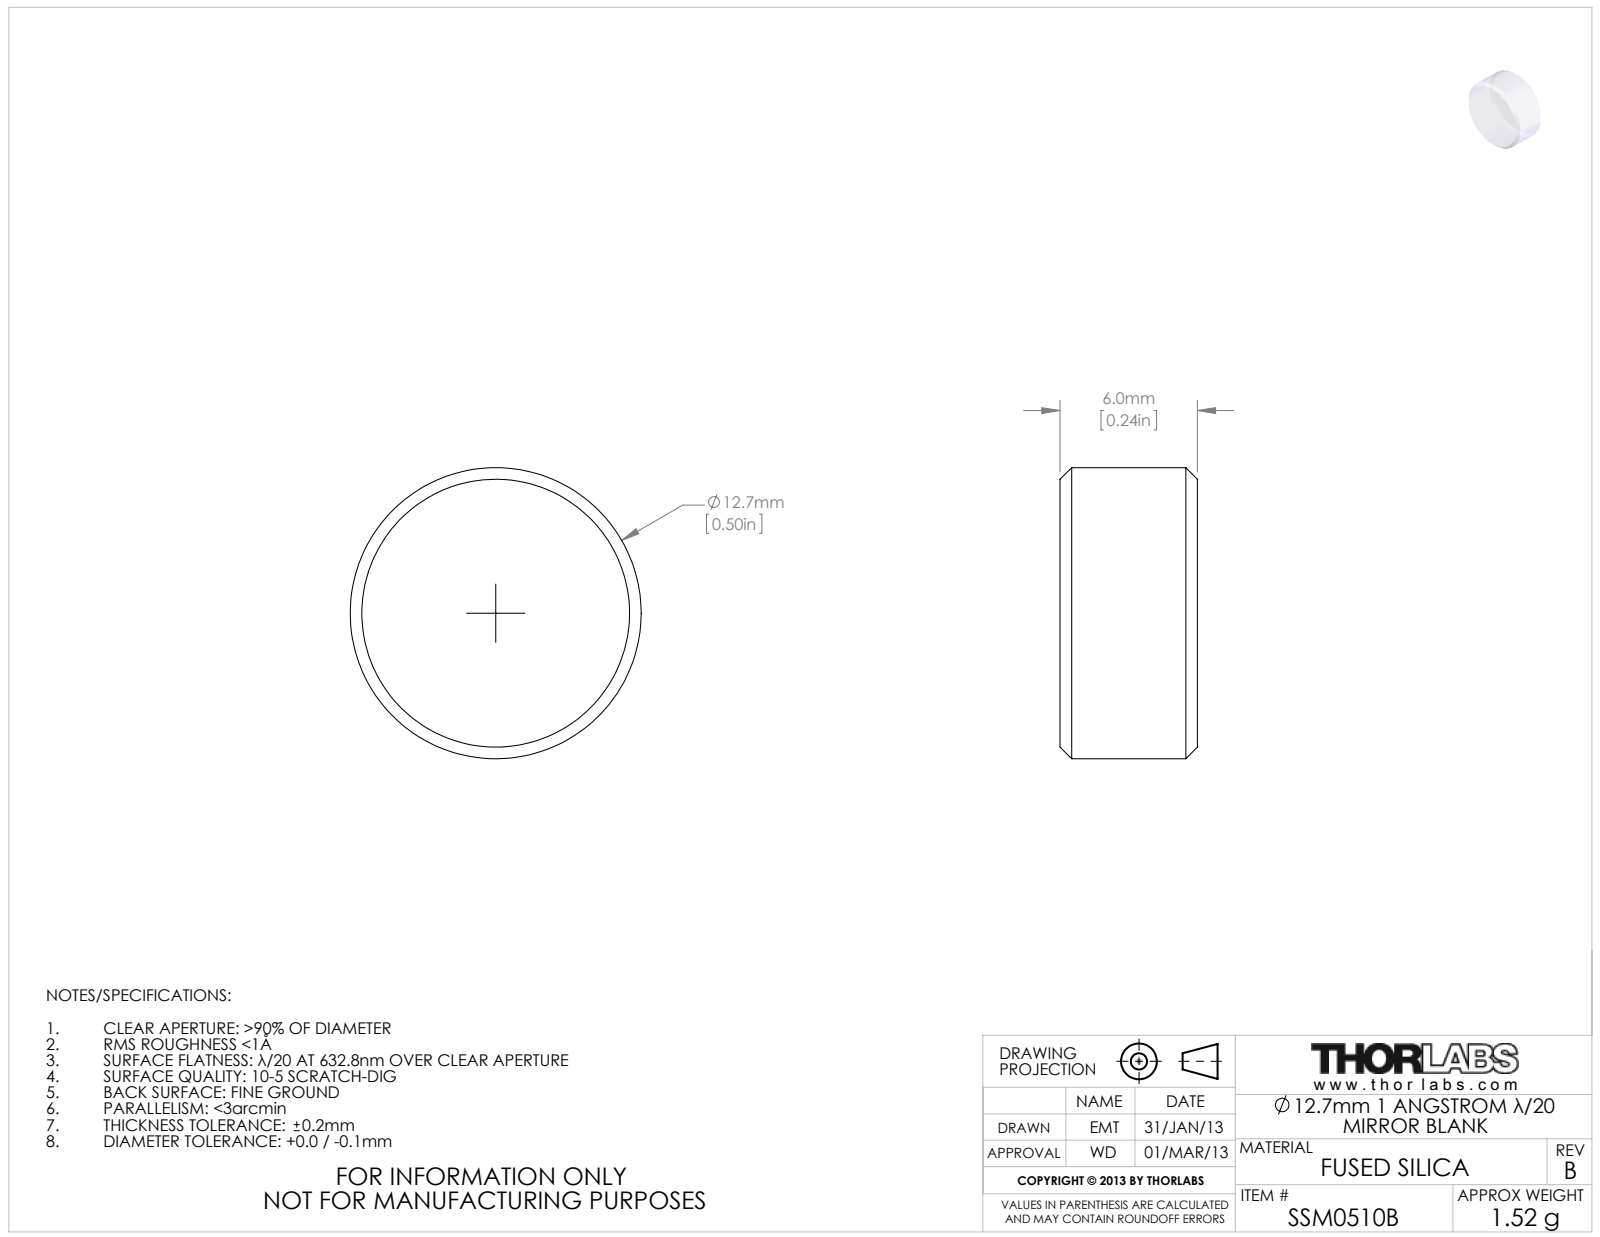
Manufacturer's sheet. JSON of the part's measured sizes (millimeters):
{"part_name": "TTN008864-E0W", "step_written_by": "SolidWorks 2012 (CONFIG_CONTROL_DESIGN)", "units": "millimeters", "bodies": {"solids": 0, "faces": 8, "planar": 2, "cylindrical": 2, "other": 4}, "overall_size": [12.7, 12.7, 6], "round_bosses_or_shafts": [[12.7, 1]], "face_to_face_distances": [6]}
